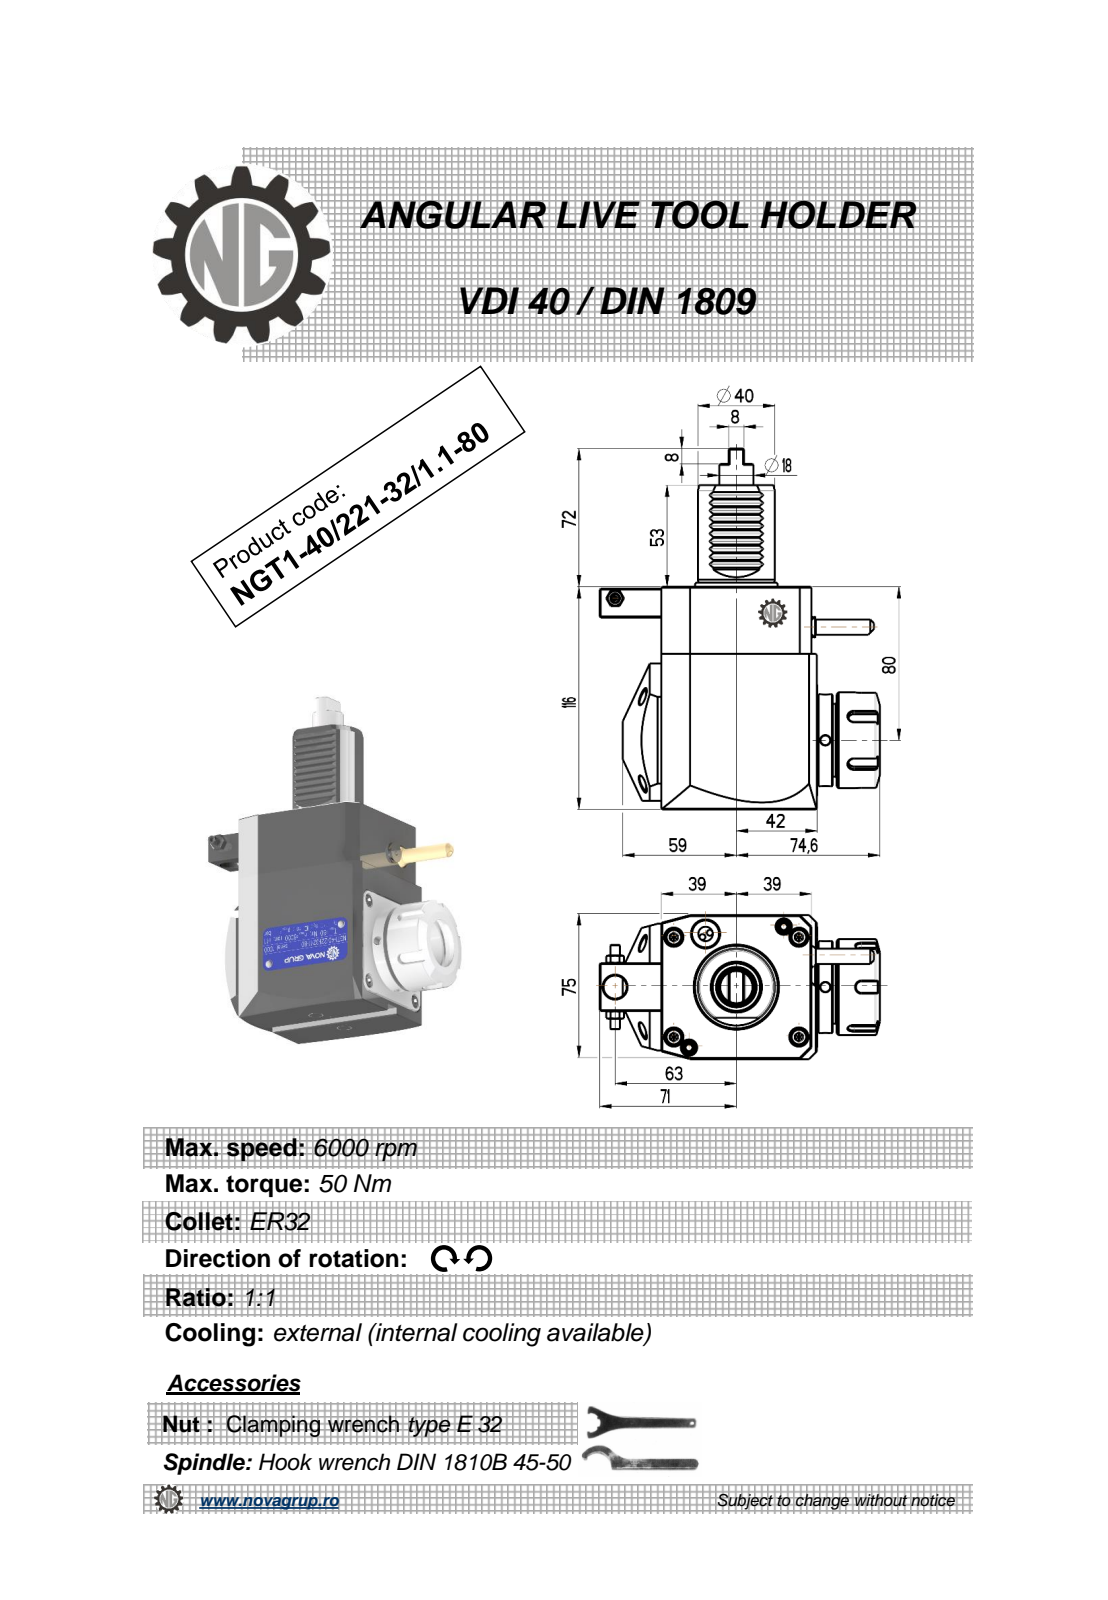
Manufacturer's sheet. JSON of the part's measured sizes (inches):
{"part_name": "NGT1_40_221_32_1_1_80", "step_written_by": "PRO/ENGINEER BY PARAMETRIC TECHNOLOGY CORPORATION, 2010280 (CONFIG_CONTROL_DESIGN)", "units": "inches", "bodies": {"solids": 1, "faces": 415, "planar": 199, "cylindrical": 89, "other": 127}, "overall_size": [7.402, 5.732, 3.016], "volume_in3": 53.15, "surface_area_in2": 108.2, "round_holes": [[0.197, 3], [0.118, 1], [0.165, 1], [0.374, 1], [0.472, 1], [1.063, 1]], "round_bosses_or_shafts": [[1.969, 1], [1.89, 1], [1.614, 1], [1.575, 1], [0.701, 1], [0.441, 1], [0.353, 1], [0.315, 1]], "partial_cylinders_radius": [[0.01, 12], [0.012, 10], [0.009, 6], [0.118, 5], [0.031, 2], [0.02, 1], [1.575, 1]], "face_to_face_distances": [2.953, 4.567, 3.189, 0.118, 3.071, 3.181, 0.11, 0.984, 0.177, 0.295], "hole_center_spacings": [0.824, 2.407, 2.854, 4.301, 5.195]}
